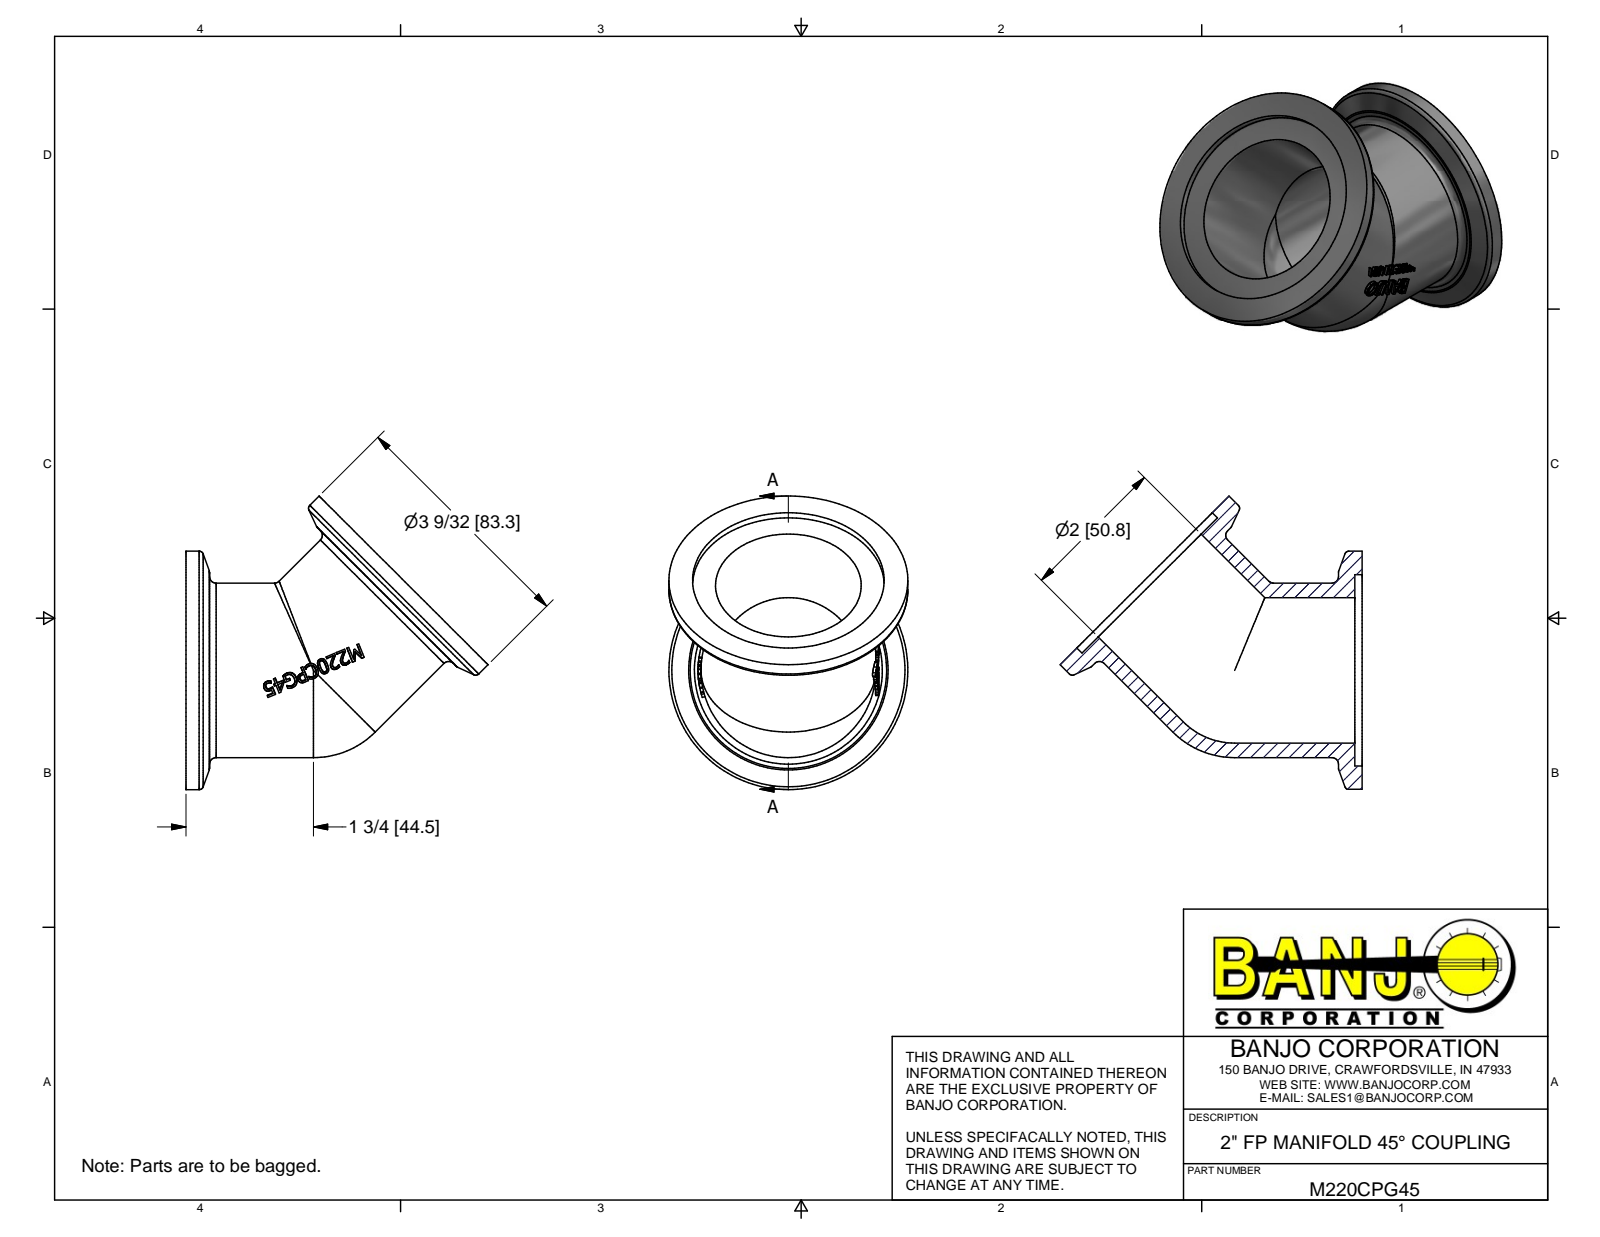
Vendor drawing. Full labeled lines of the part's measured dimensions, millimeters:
Part name (STEP PRODUCT): M220CPG45
STEP written by: Autodesk Inventor 2012 (AUTOMOTIVE_DESIGN)
Units: millimetres
Bodies: 3 solids, 400 faces (6 planar, 50 cylindrical, 344 other)
Overall size (bounding box): 105.3 × 102.3 × 83.1
Volume: 108 500 mm³ · Surface area: 43 130 mm²
Round holes (diameter × count): ⌀50.8 ×2, ⌀66.8 ×2, ⌀61 ×1
Round bosses / shafts (diameter × count): ⌀83.1 ×2, ⌀61 ×1
Partial cylindrical surfaces — rounded edges, fillets, slot ends (radius × count): R31.5 ×2
Main face-to-face distances: 2.5, 5.7, 8.2, 8.2, 5.7
